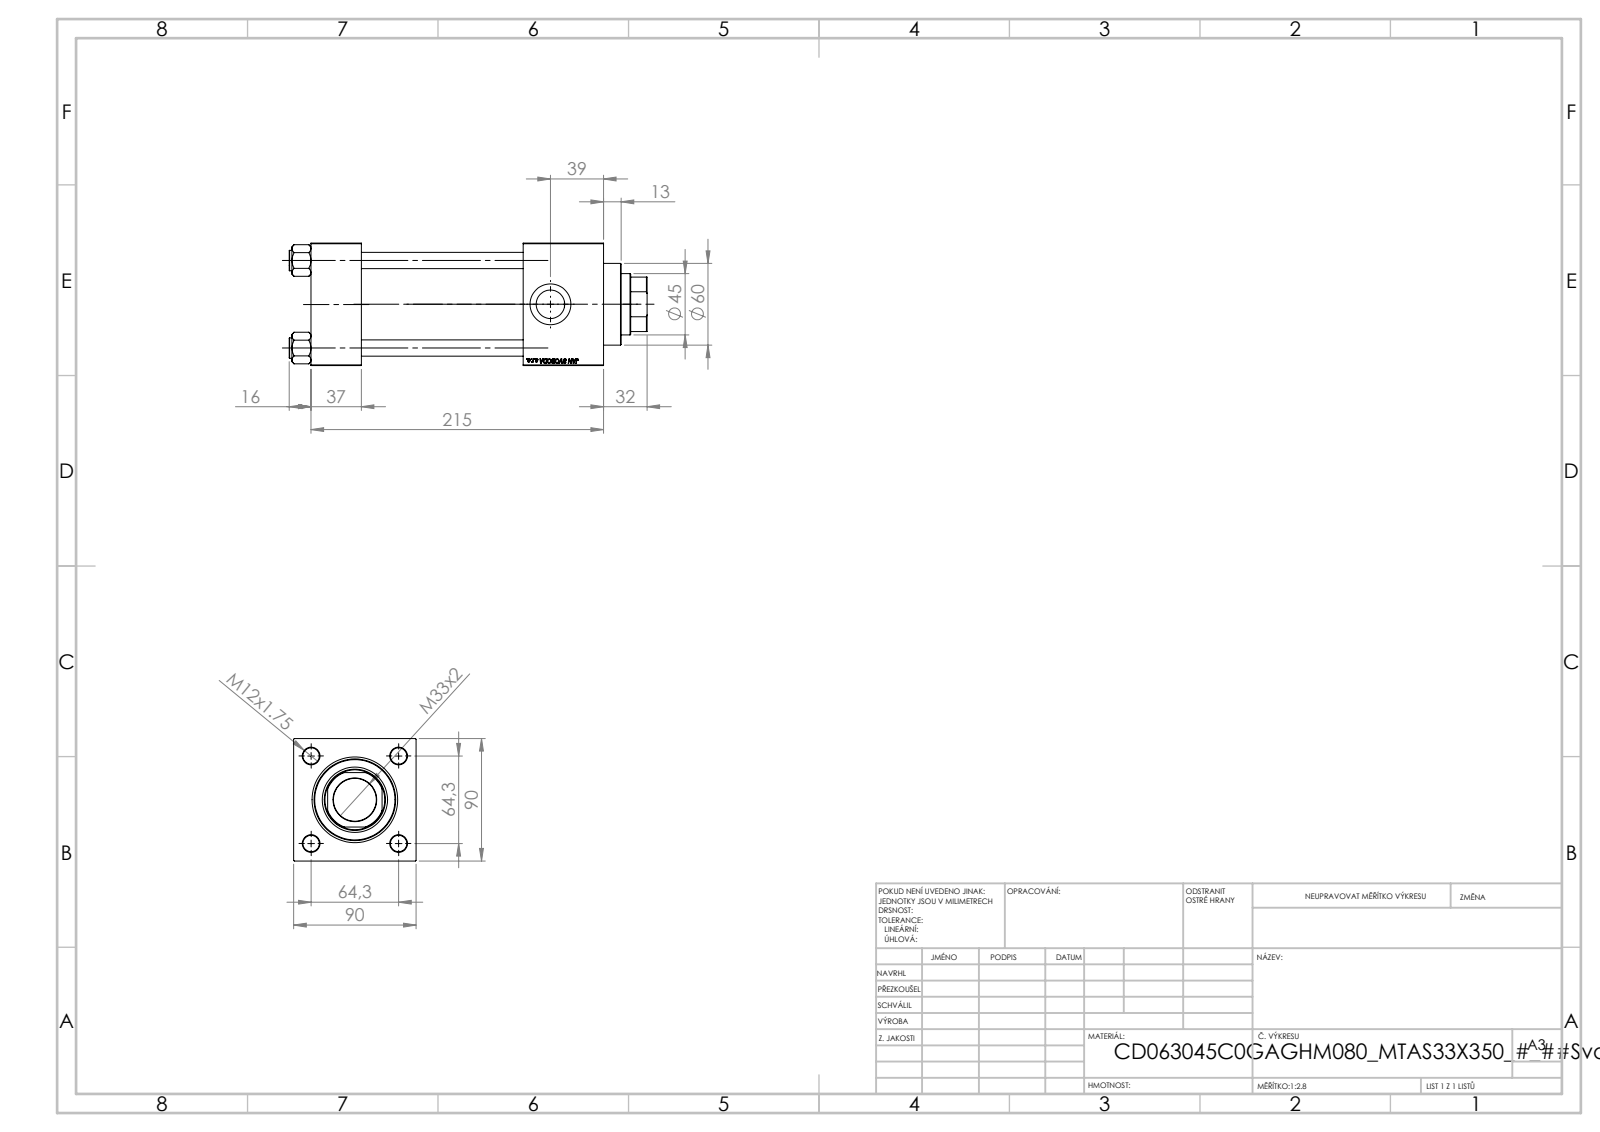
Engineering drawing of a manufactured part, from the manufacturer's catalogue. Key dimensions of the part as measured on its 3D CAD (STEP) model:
Part name (STEP PRODUCT): V215CD_VCP_C; V215CD_VC_C; V215CD_C_TYCINKA; V215CD_Body_C (+1 more)
STEP written by: SolidWorks 2019 (CONFIG_CONTROL_DESIGN)
Units: millimetres
Bodies: 11 solids, 1146 faces (525 planar, 85 cylindrical, 536 other)
Overall size (bounding box): 263 × 90 × 90
Volume: 1 158 000 mm³ · Surface area: 232 347 mm²
Round holes (diameter × count): ⌀12 ×4, ⌀7 ×2, ⌀20.96 ×2, ⌀30 ×2, ⌀31.5 ×1, ⌀45 ×1, ⌀48 ×1, ⌀50 ×1, ⌀60 ×1, ⌀63 ×1
Round bosses / shafts (diameter × count): ⌀15 ×4, ⌀69 ×1
Partial cylindrical surfaces — rounded edges, fillets, slot ends (radius × count): R22 ×1
Main face-to-face distances: 90, 37, 59, 156, 119, 215, 178, 186.3, 149.3, 30.3
Hole centre spacings: 45.47, 64.3, 90.93
